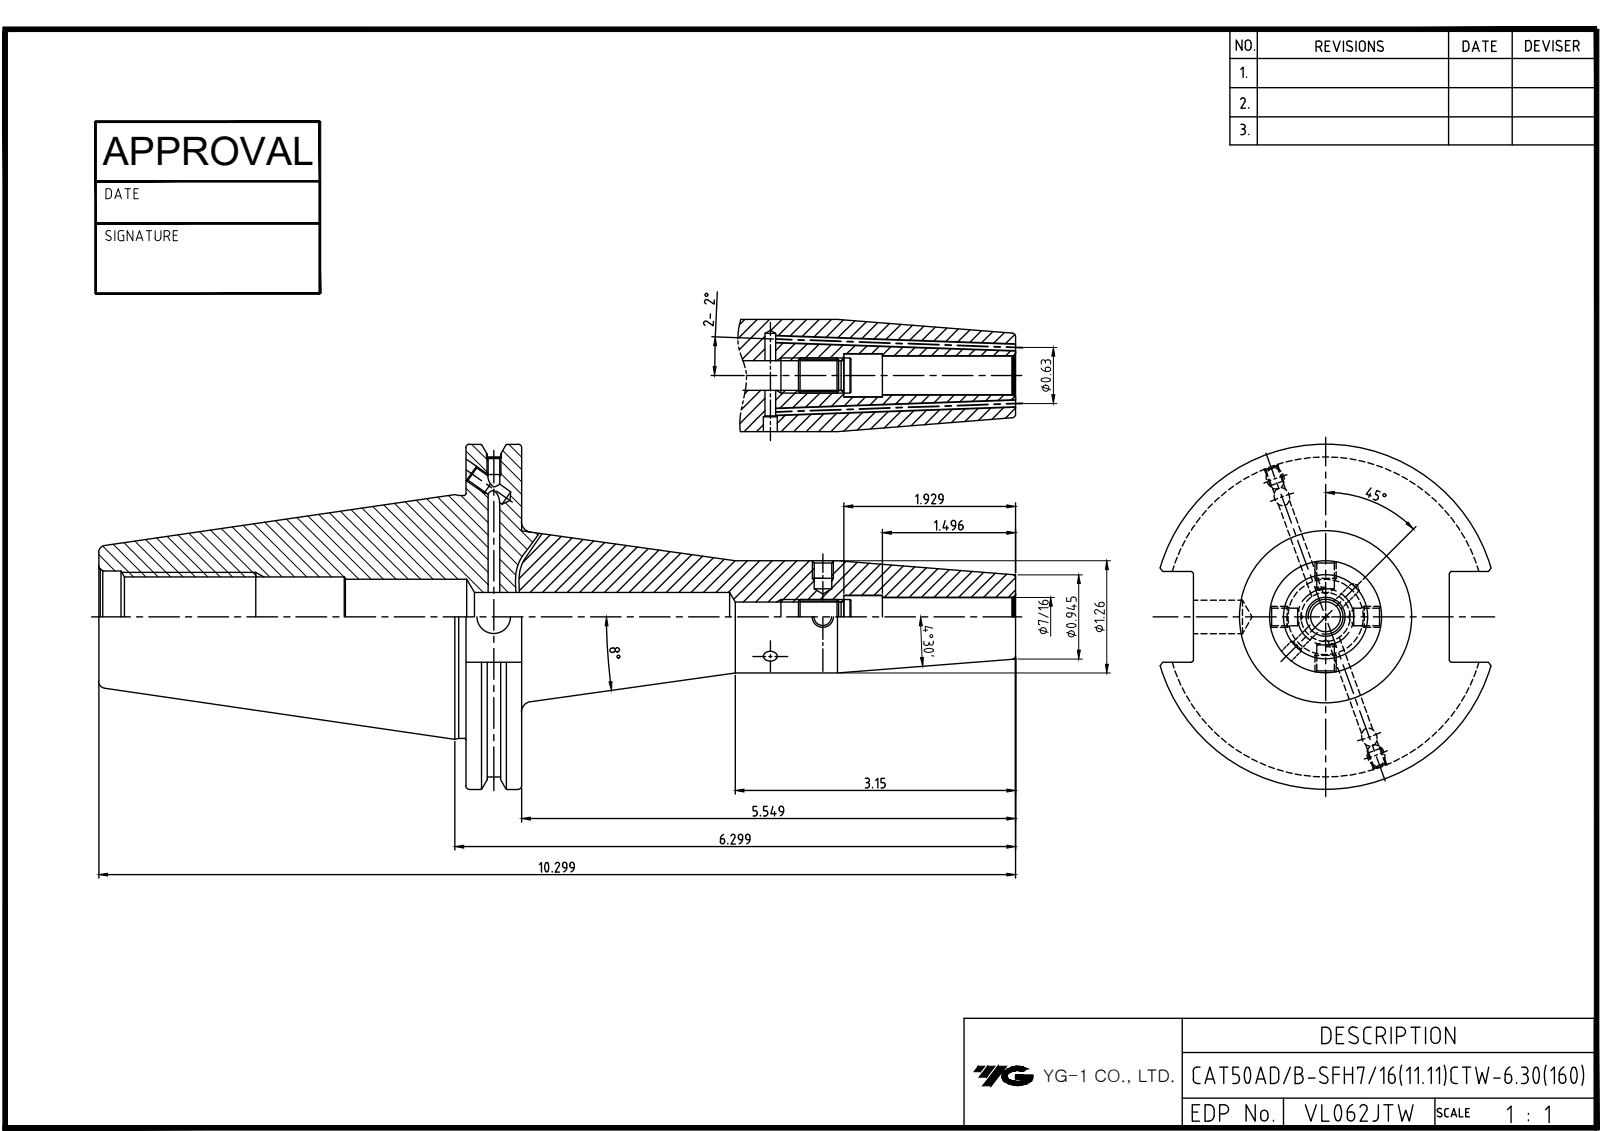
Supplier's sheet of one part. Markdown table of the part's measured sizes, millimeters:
| quantity | value |
| --- | --- |
| part name | LO-CAT50ADB-SFH11.1125CTW-160 |
| STEP written by | Autodesk Inventor 2022 (AUTOMOTIVE_DESIGN) |
| units | millimeters |
| bodies | 1 solid, 93 faces (37 planar, 30 cylindrical, 26 other) |
| overall size | 261.6 × 98.42 × 94.69 |
| volume | 437 853 mm³ |
| surface area | 64 712 mm² |
| round holes (diameter × count) | 2.5 × 2, 3.24 × 2, 4.13 × 2, 4.2 × 2, 5 × 2, 8.92 × 1, 9.53 × 1, 11.11 × 1, 12.31 × 1, 14 × 1, 21.5 × 1, 21.97 × 1 |
| round bosses / shafts (diameter × count) | 98.42 × 1, 91.29 × 1, 69.25 × 1, 32 × 1 |
| main face-to-face distances | 15.88, 104.77, 120.65, 73.03, 25.9, 261.6, 156.83, 140.95, 110.82, 6.05 |
